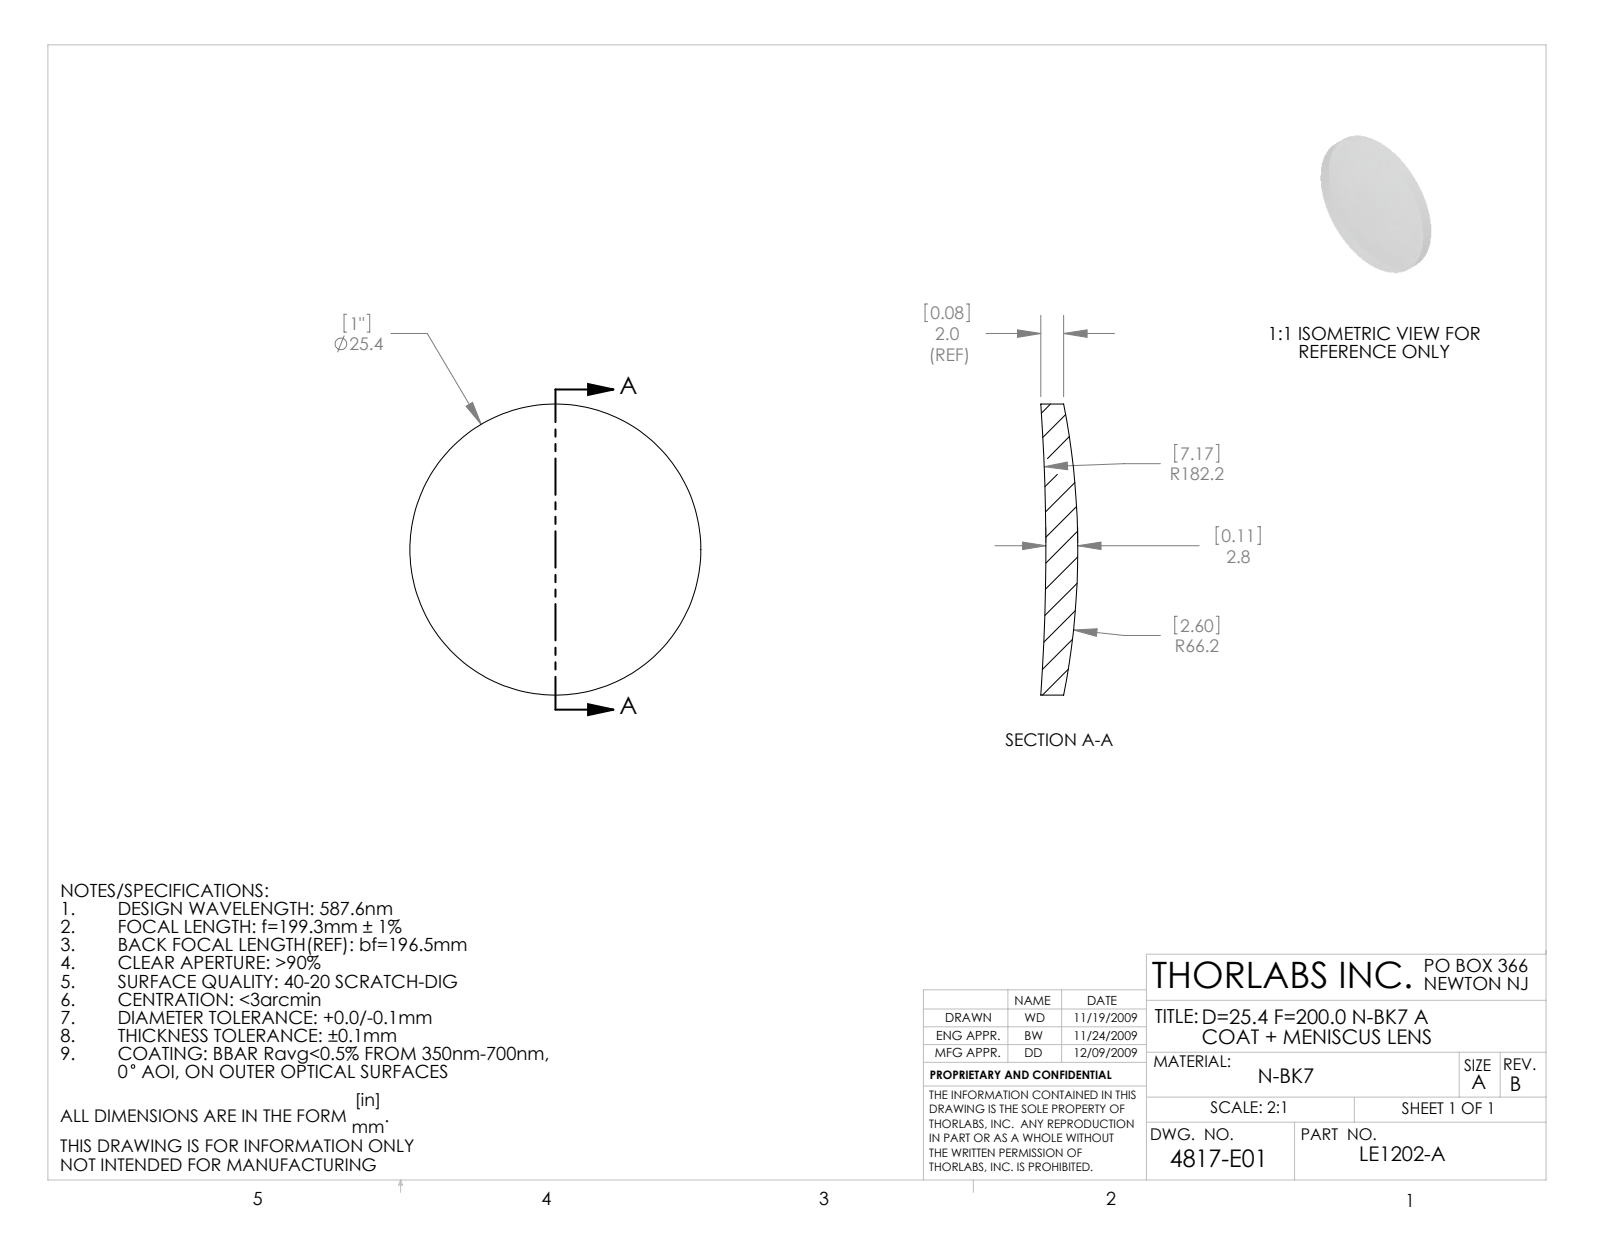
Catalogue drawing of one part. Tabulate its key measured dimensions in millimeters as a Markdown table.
| quantity | value |
| --- | --- |
| part name | 4817-E0W |
| STEP written by | SolidWorks 2009 (AUTOMOTIVE_DESIGN) |
| units | millimeters |
| bodies | 1 solid, 6 faces (0 planar, 2 cylindrical, 4 other) |
| overall size | 25.4 × 25.4 × 3.23 |
| volume | 1 215 mm³ |
| surface area | 1 179 mm² |
| round bosses / shafts (diameter × count) | 25.4 × 1 |
